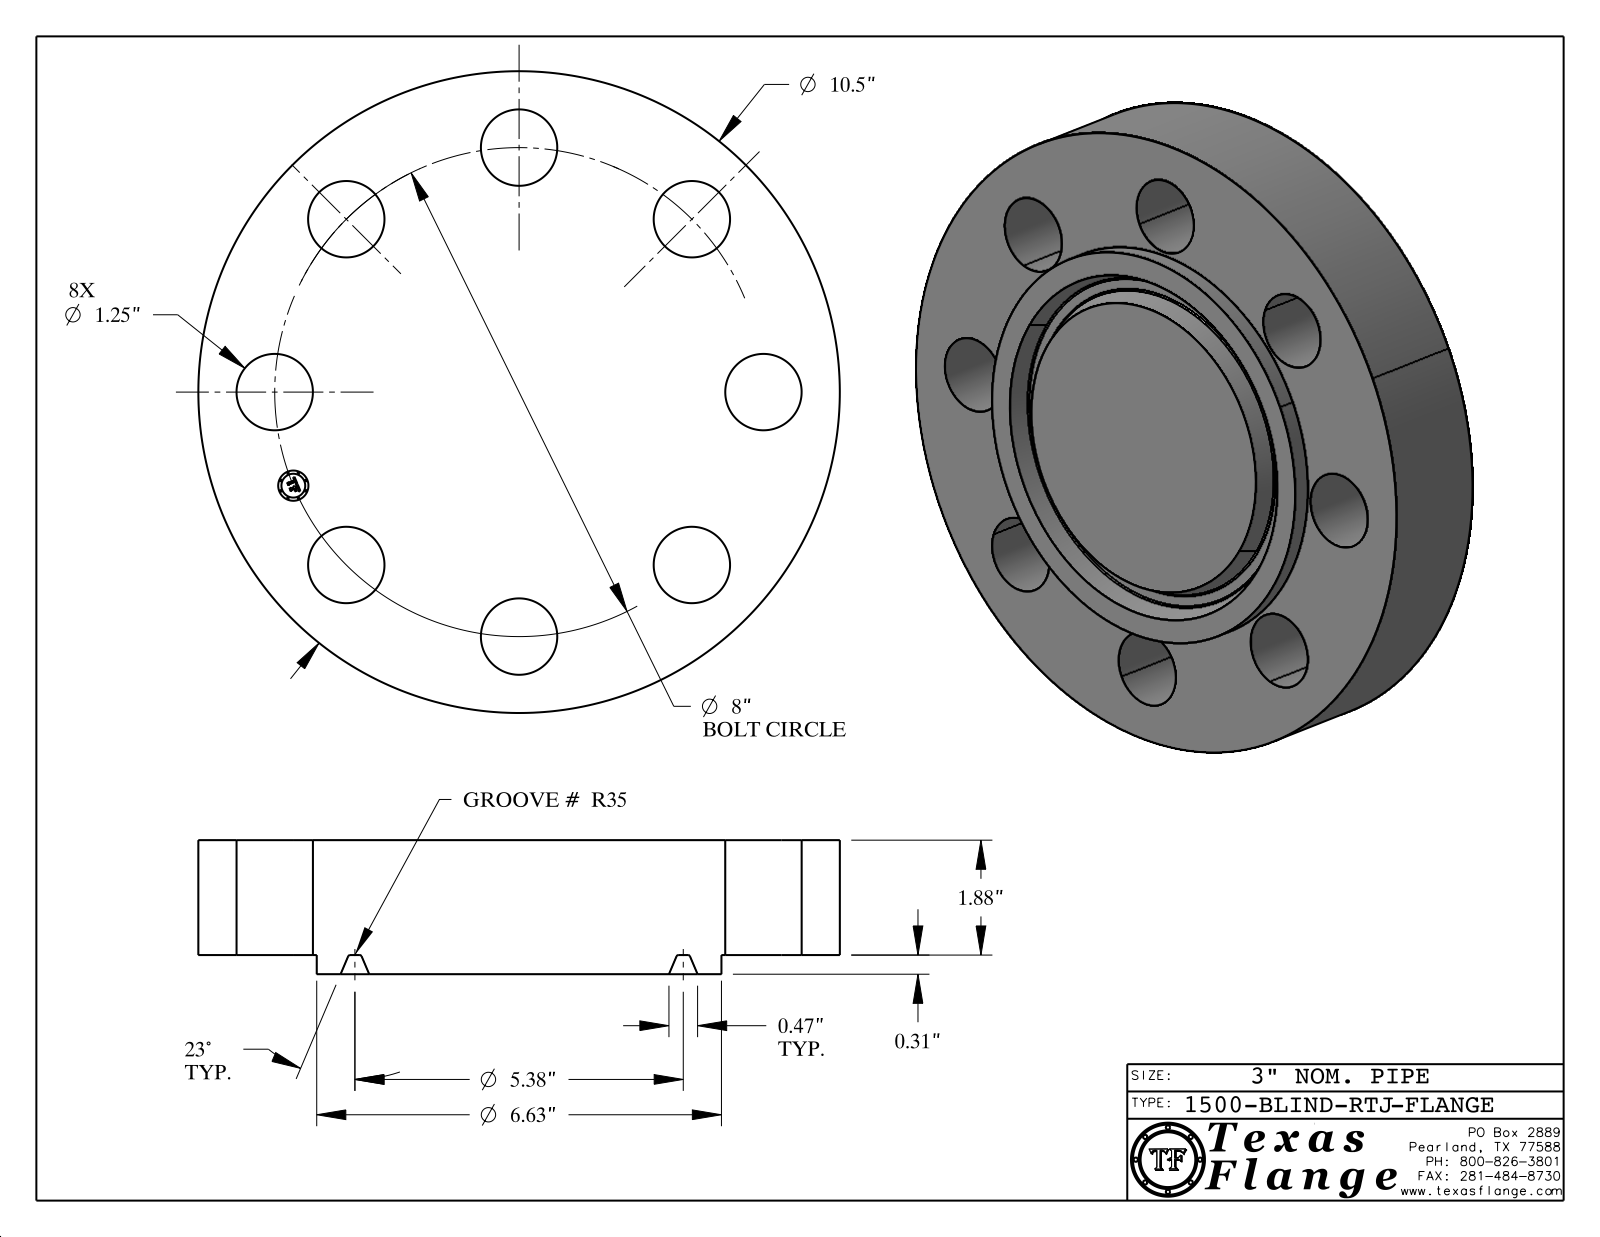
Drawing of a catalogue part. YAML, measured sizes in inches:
part_name: "1500-BLIND-RTJ"
step_written_by: "CATIA V5 STEP AP214 (AUTOMOTIVE_DESIGN)"
units: inches
bodies: {solids: 1, faces: 418, planar: 370, cylindrical: 40, other: 8}
overall_size: [10.5, 10.5, 2.193]
volume: 153.3
surface_area: 288.1
round_holes:
  - {diameter: 1.25, count: 8}
  - {diameter: 0.495, count: 1}
round_bosses_or_shafts:
  - {diameter: 0.03, count: 8}
  - {diameter: 10.5, count: 1}
  - {diameter: 6.625, count: 1}
  - {diameter: 0.39, count: 1}
face_to_face_distances: [1.88, 0.313, 2.193, 0.015, 2.178, 1.865, 0.148, 0.145, 0.027, 0.096]
hole_center_spacings: [3.061, 5.657, 7.391, 1.561, 6.652, 7.846, 8, 8]
